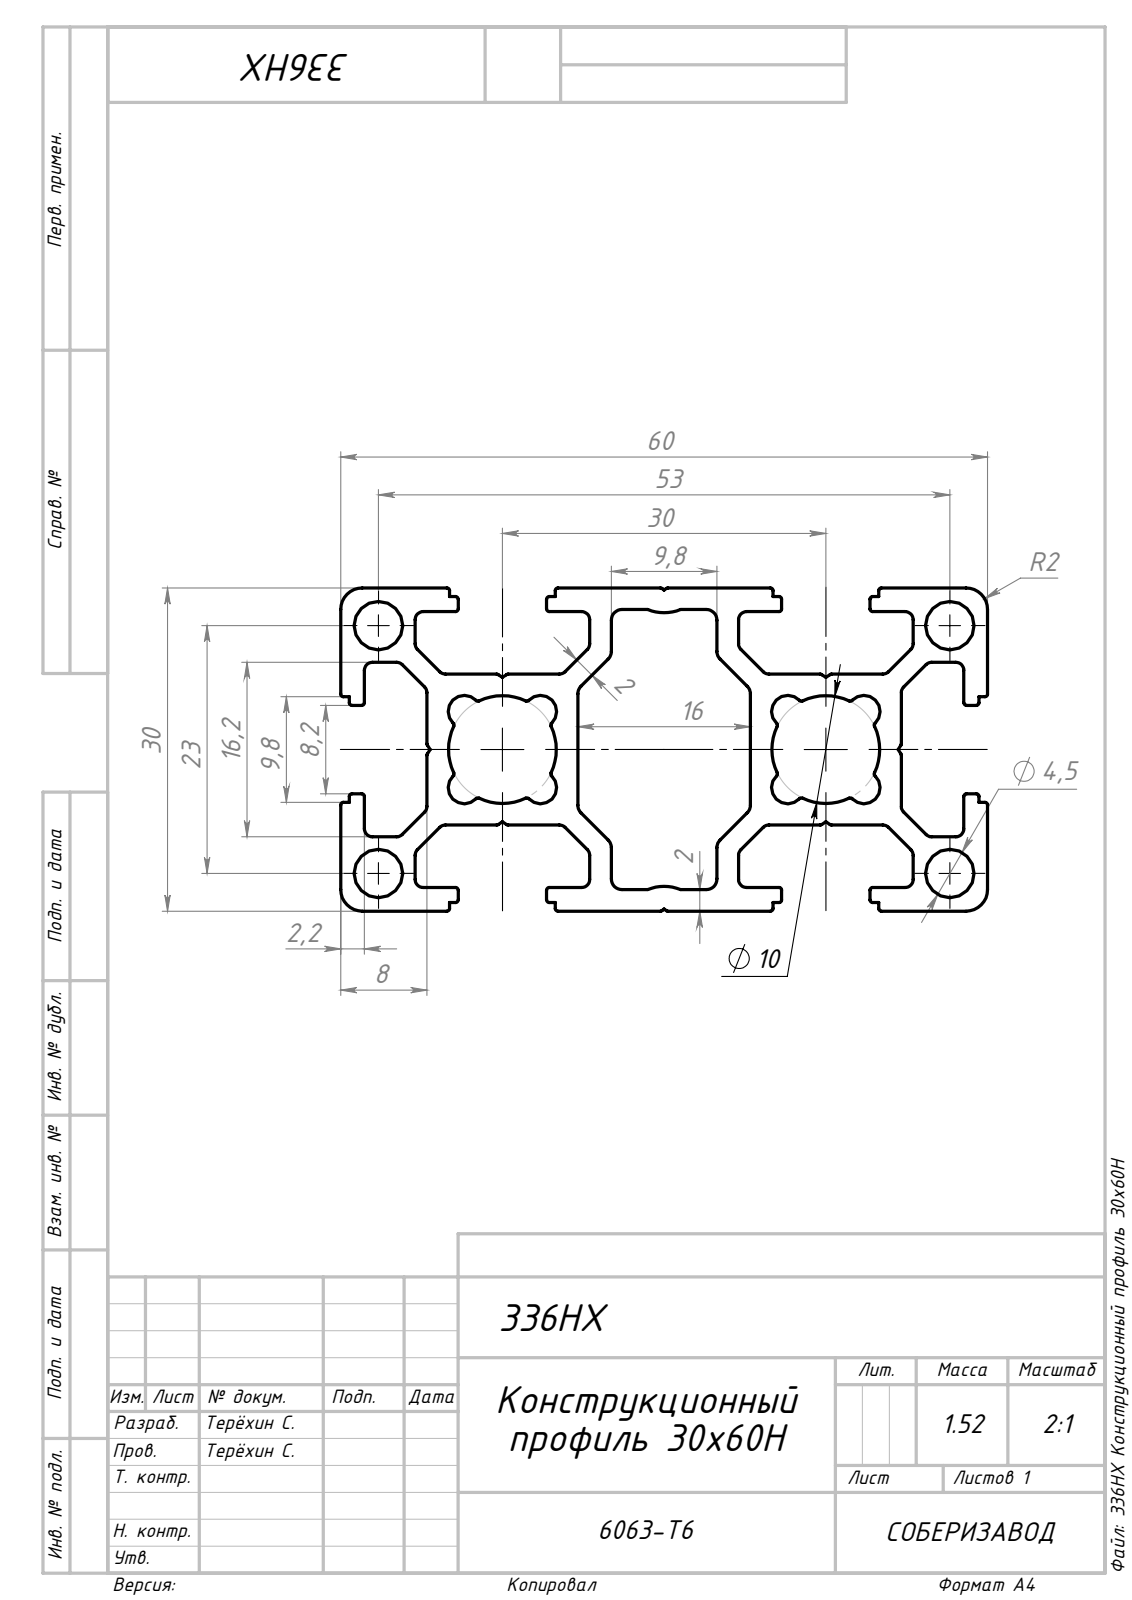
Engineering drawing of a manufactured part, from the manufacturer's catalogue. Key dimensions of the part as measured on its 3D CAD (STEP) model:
Part name (STEP PRODUCT): 336X Конструкционный профиль 30х60
STEP written by: SolidWorks 2019 (AUTOMOTIVE_DESIGN)
Units: millimetres
Bodies: 1 solid, 284 faces (128 planar, 156 cylindrical, 0 other)
Overall size (bounding box): 1000 × 60 × 30
Volume: 563 062 mm³ · Surface area: 555 271 mm²
Round holes (diameter × count): ⌀4.5 ×4
Partial cylindrical surfaces — rounded edges, fillets, slot ends (radius × count): R0.25 ×68, R0.75 ×36, R1 ×12, R1.5 ×8, R2 ×4, R4 ×2, R5 ×2
Main face-to-face distances: 30, 22, 8, 2, 14, 2.2, 5.8, 19.8, 1.1, 15.1
Hole centre spacings: 23, 53, 57.78
